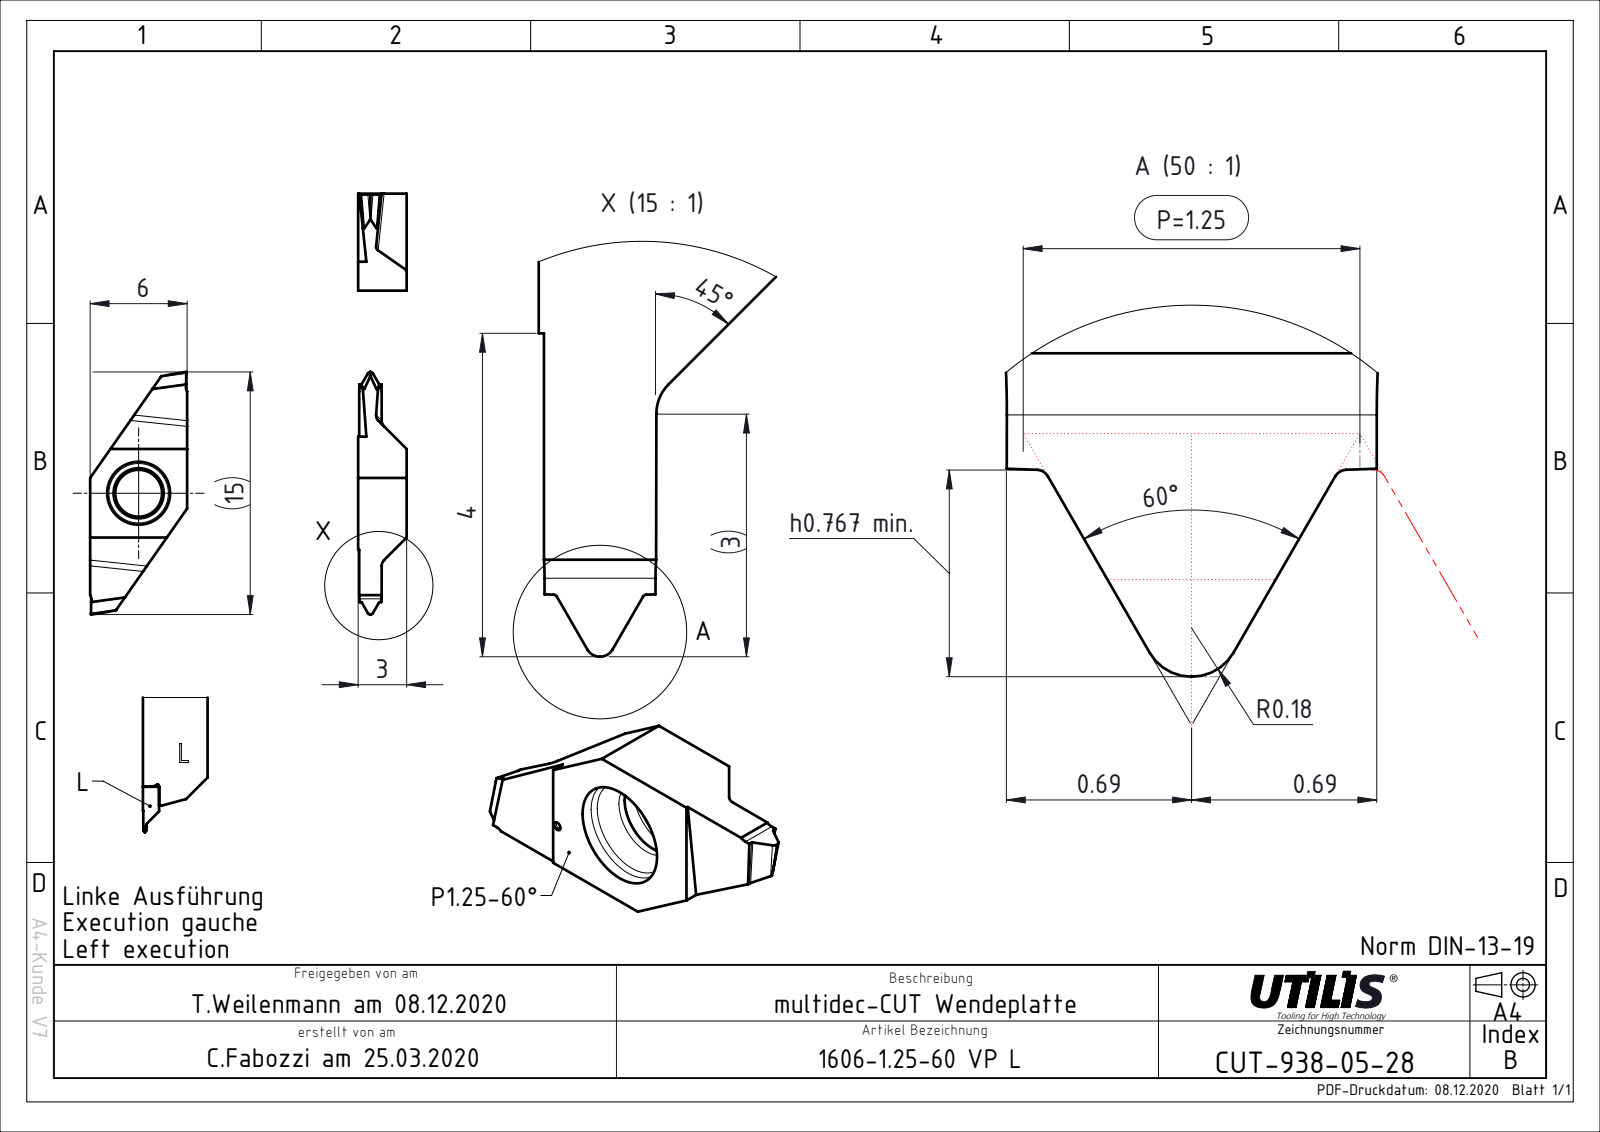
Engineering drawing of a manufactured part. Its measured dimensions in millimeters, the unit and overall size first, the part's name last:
Units: millimetres
Overall size (bounding box): 15 × 6 × 3
Round holes (diameter × count): ⌀2.9 ×1
Partial cylindrical surfaces — rounded edges, fillets, slot ends (radius × count): R0.18 ×4, R0.5 ×2
Main face-to-face distances: 6, 3, 1.22, 11.29, 9, 12, 7, 12.01, 12.02
Volume: 121 mm³ · Surface area: 209 mm²
Bodies: 1 solid, 42 faces (24 planar, 14 cylindrical, 4 other)
Part name (STEP PRODUCT): CUT-938-05; ASME Y14.5
STEP written by: FormatWorks Professional (AP242_MANAGED_MODEL_BASED_3D_ENGINEERING_MIM_LF)
